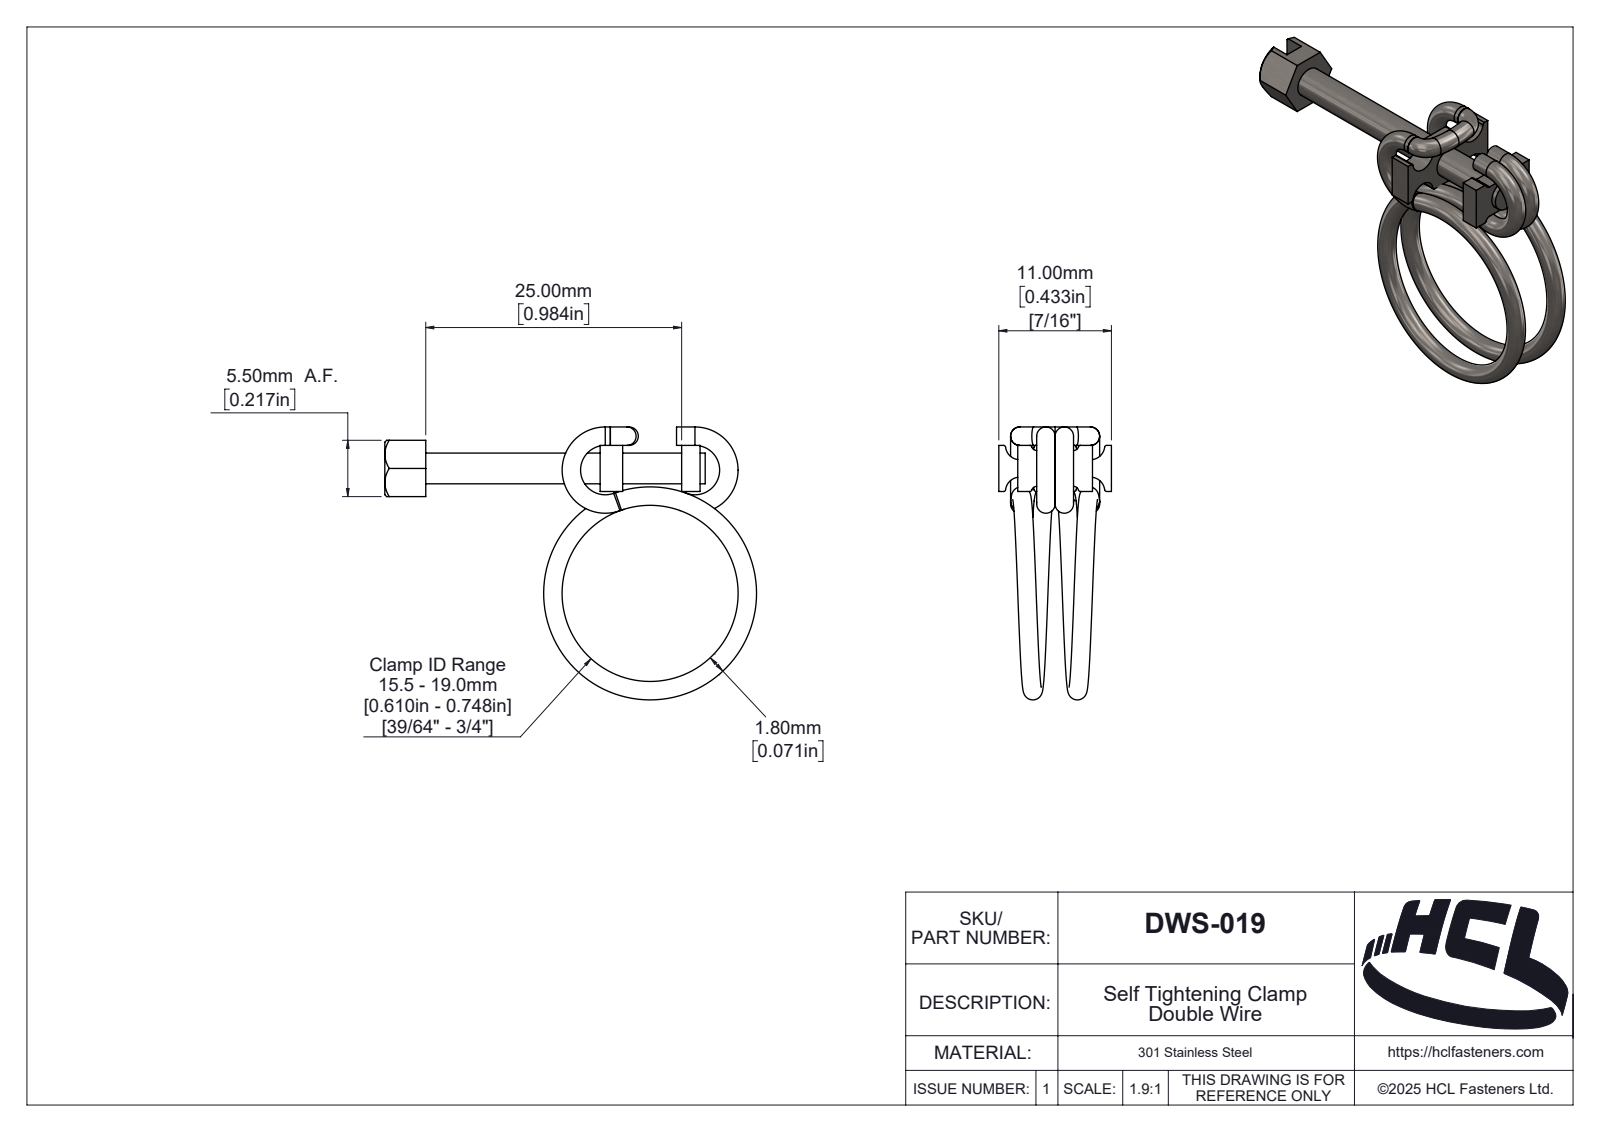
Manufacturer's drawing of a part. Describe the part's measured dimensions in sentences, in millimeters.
The part is named "DWS-019". Its 3-D file was written by "SolidWorks 2025 (AUTOMOTIVE_DESIGN)". It is 6 solids with 209 faces: 51 planar, 74 cylindrical and 84 other. Overall it measures 36.32 by 26.65 by 11 millimeters. Its volume is 870 cubic millimeters and its surface area 1 767 square millimeters. Round holes: 1 of diameter 3. Round bosses or shafts: 4 of diameter 1.8. Partial cylindrical surfaces (rounded edges, fillets, slot ends): 12 of radius 0.2, 4 of radius 0.5, 4 of radius 1.4, 1 of radius 0.4, 1 of radius 0.51, 1 of radius 0.53, 1 of radius 0.64, 1 of radius 0.91. The main face-to-face distances are 4.5, 0.5, 2, 5.5, 2.2, 4, 1, 7.96, 5.76, 9.76.
